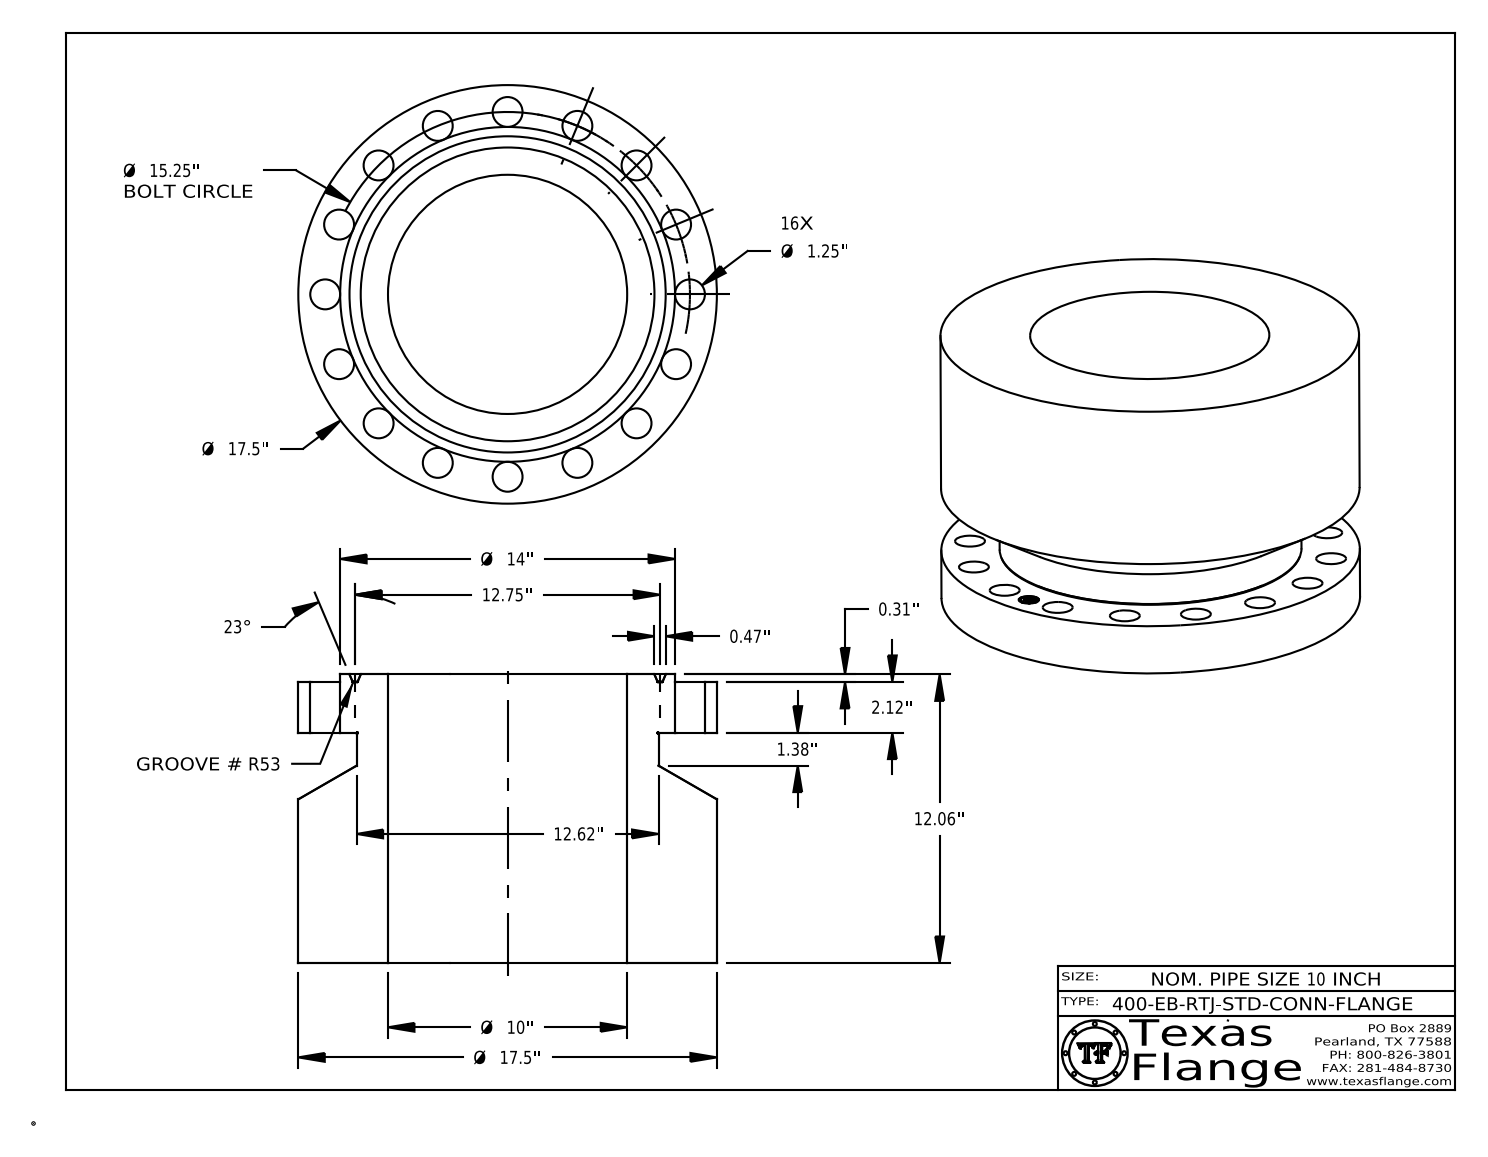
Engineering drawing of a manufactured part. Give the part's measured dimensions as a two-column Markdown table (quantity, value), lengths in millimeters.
| quantity | value |
| --- | --- |
| part name | 10-400-EB-RTJ-STD-CONN-FLANGE |
| STEP written by | CATIA V5 STEP AP214 (AUTOMOTIVE_DESIGN) |
| units | millimeters |
| bodies | 1 solid, 447 faces (371 planar, 62 cylindrical, 14 other) |
| overall size | 444.5 × 444.5 × 306.4 |
| volume | 26 810 000 mm³ |
| surface area | 1 048 000 mm² |
| round holes (diameter × count) | 31.8 × 16, 21.6 × 1, 254 × 1 |
| round bosses / shafts (diameter × count) | 1.3 × 8, 444.5 × 1, 355.6 × 1, 320.5 × 1, 17 × 1 |
| main face-to-face distances | 244.6, 53.8, 298.5, 8, 61.8, 306.4, 61.7, 53.7, 244.7, 6.5 |
| hole center spacings | 215.2, 273.9, 379.9, 357.9, 193.7, 75.6, 75.6, 148.2 |
